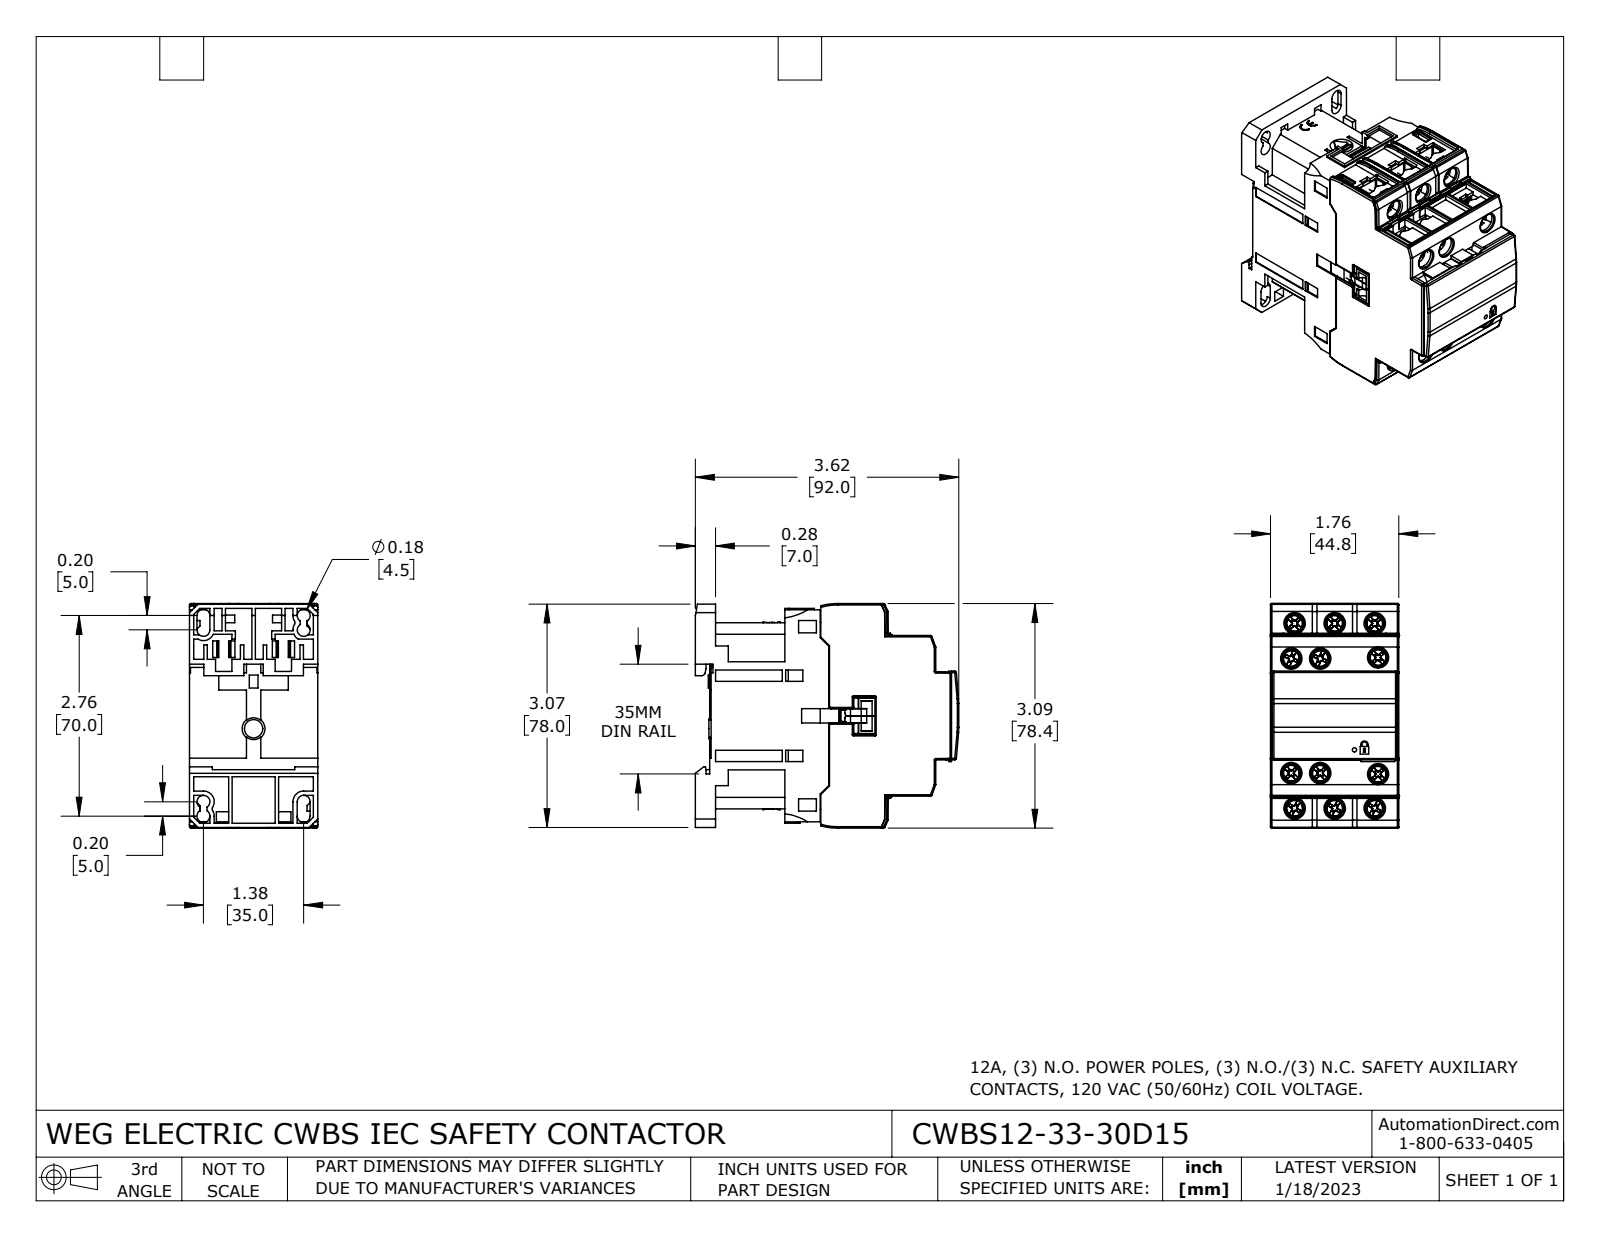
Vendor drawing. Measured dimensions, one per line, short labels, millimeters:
name: CWBS12-33-30D15
written by: SolidWorks 2021 (CONFIG_CONTROL_DESIGN)
unit: mm
bodies: 45 solids, 3295 faces (2311 planar, 624 cylindrical, 360 other)
size: 91.9 × 78.4 × 44.8
volume: 221 400 mm³; area: 77 680 mm²
holes: 12× ⌀3.1, 6× ⌀6.5, 4× ⌀4.5, 1× ⌀1.5
bosses: 12× ⌀4.3, 12× ⌀3.5, 8× ⌀2.7, 4× ⌀2.7
rounds: 139× R0.5, 52× R0.3, 24× R1.8, 24× R24.5, 24× R54.1, 20× R0.4, 19× R1, 11× R2.7
face distances: 44.8, 1.2, 43.6, 83.9, 44.6, 39.4, 7, 0.6, 45.1, 38.9
hole spacings: 14, 28, 5, 10.1, 20.2, 30.3, 34.1, 40
